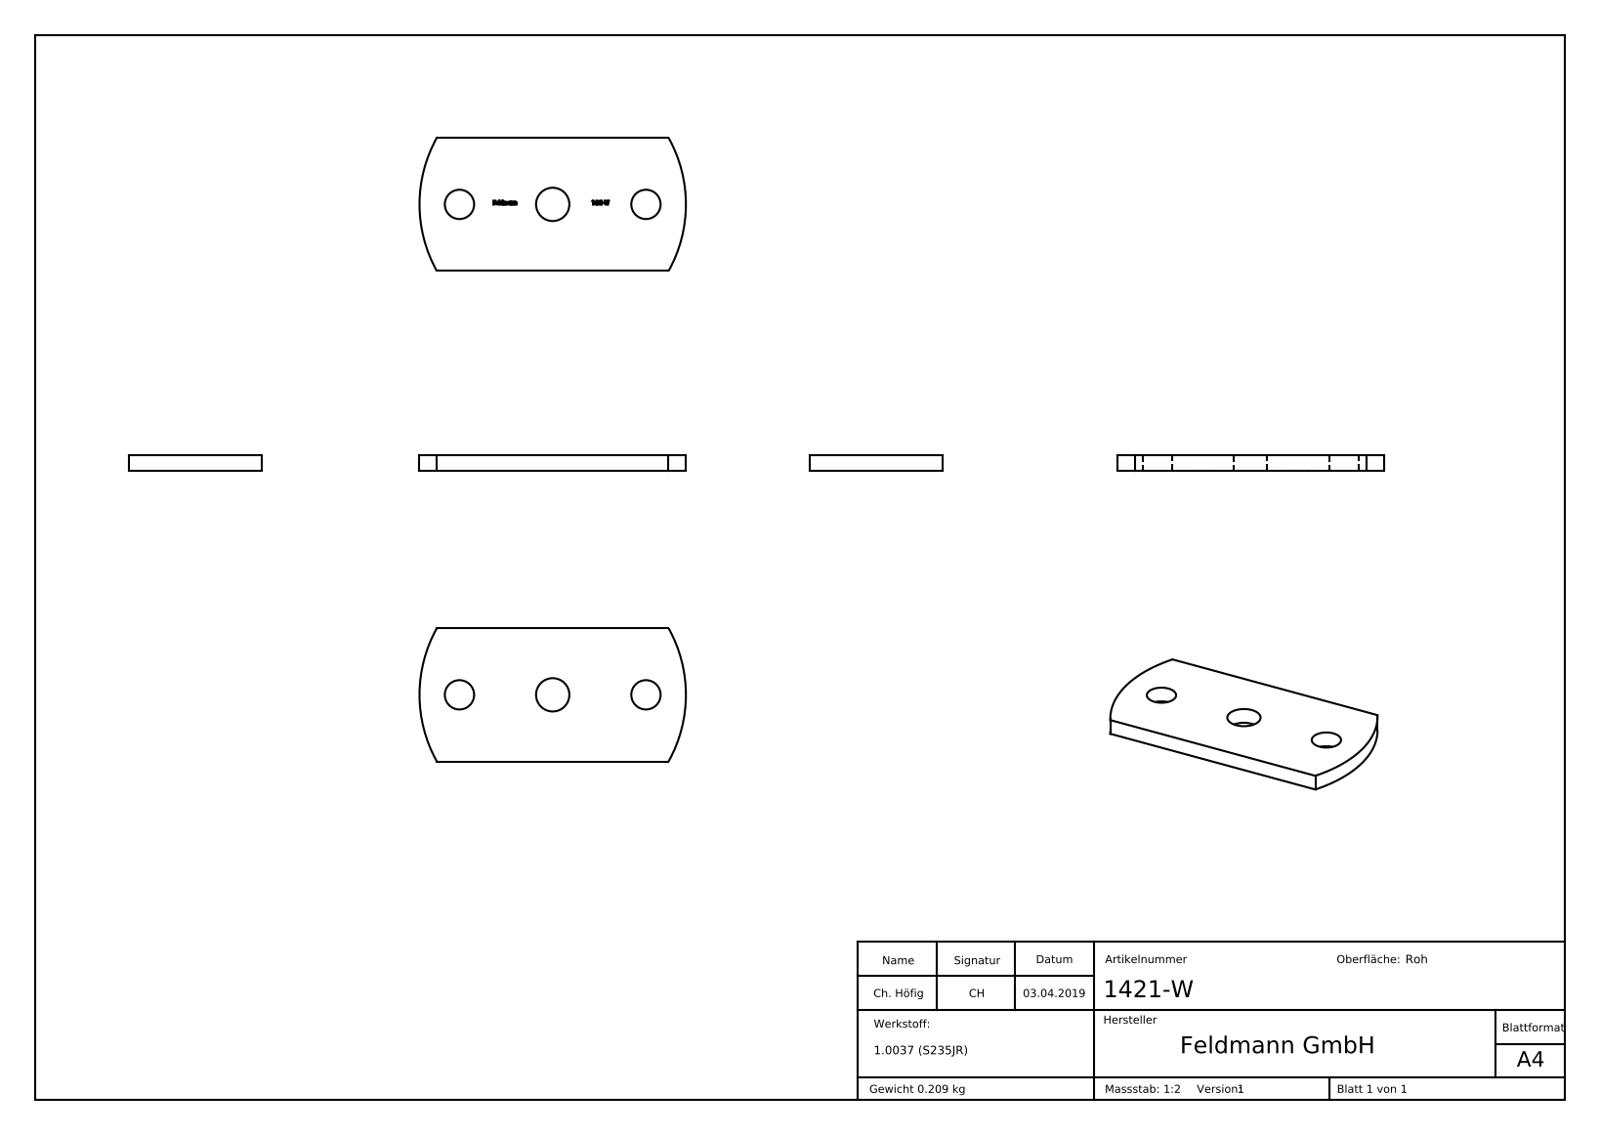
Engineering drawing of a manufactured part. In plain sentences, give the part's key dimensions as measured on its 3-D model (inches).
The part is named "1421-W". Its 3-D file was written by "SolidWorks 2015 (CONFIG_CONTROL_DESIGN)". It is 1 solid with 186 faces: 124 planar, 8 cylindrical and 54 other. Overall it measures 3.937 by 1.969 by 0.236 inches. Its volume is 1.639 cubic inches and its surface area 17.49 square inches. Round holes: 2 of diameter 0.433, 1 of diameter 0.492. Partial cylindrical surfaces (rounded edges, fillets, slot ends): 2 of radius 2.021. The main face-to-face distances are 0.236, 1.969, 0.232, 1.389, 1.51, 0.12, 0.049, 0.08, 1.469, 1.59. The hole center spacings are 1.378, 2.756.
